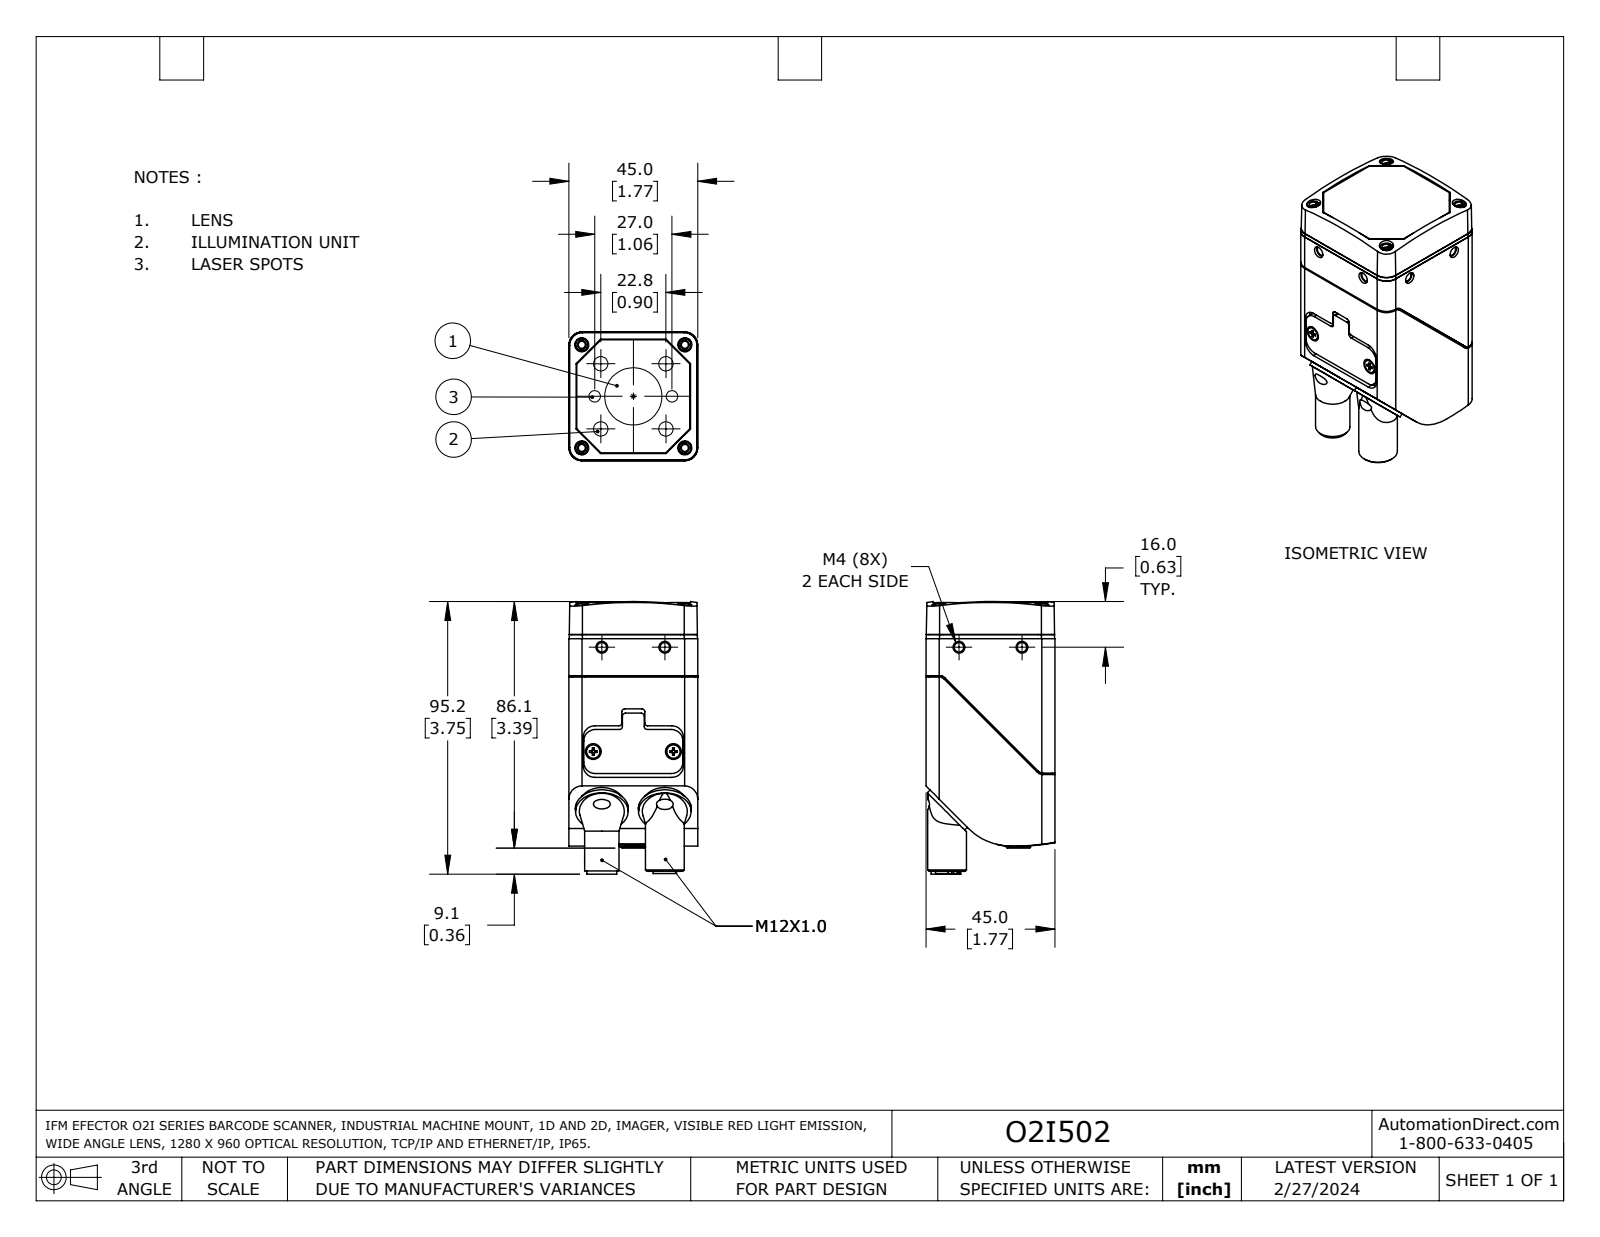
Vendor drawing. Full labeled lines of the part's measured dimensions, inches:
Part name (STEP PRODUCT): O2I5xx
STEP written by: SolidWorks 2023 (AUTOMOTIVE_DESIGN)
Units: inches
Bodies: 1 solid, 335 faces (198 planar, 117 cylindrical, 20 other)
Overall size (bounding box): 3.746 × 1.772 × 1.772
Volume: 9.97 in³ · Surface area: 40.04 in²
Round holes (diameter × count): ⌀0.098 ×4, ⌀0.122 ×4, ⌀0.13 ×4, ⌀0.161 ×4, ⌀0.728 ×2, ⌀0.327 ×1, ⌀0.43 ×1
Round bosses / shafts (diameter × count): ⌀0.173 ×4, ⌀0.724 ×2, ⌀0.185 ×2, ⌀0.079 ×2, ⌀0.531 ×1, ⌀0.472 ×1, ⌀0.409 ×1, ⌀0.331 ×1
Partial cylindrical surfaces — rounded edges, fillets, slot ends (radius × count): R0.181 ×12, R0.012 ×10, R0.039 ×10, R0.157 ×4, R0.157 ×4, R0.197 ×4, R0.098 ×3, R0.039 ×2
Main face-to-face distances: 1.772, 1.768, 0.016, 1.673, 0.098, 1.565, 0.108, 1.663, 1.358, 0.059
Hole centre spacings: 0.866, 1.417, 2.004, 0.292, 0.298, 1.146, 1.147, 1.334
